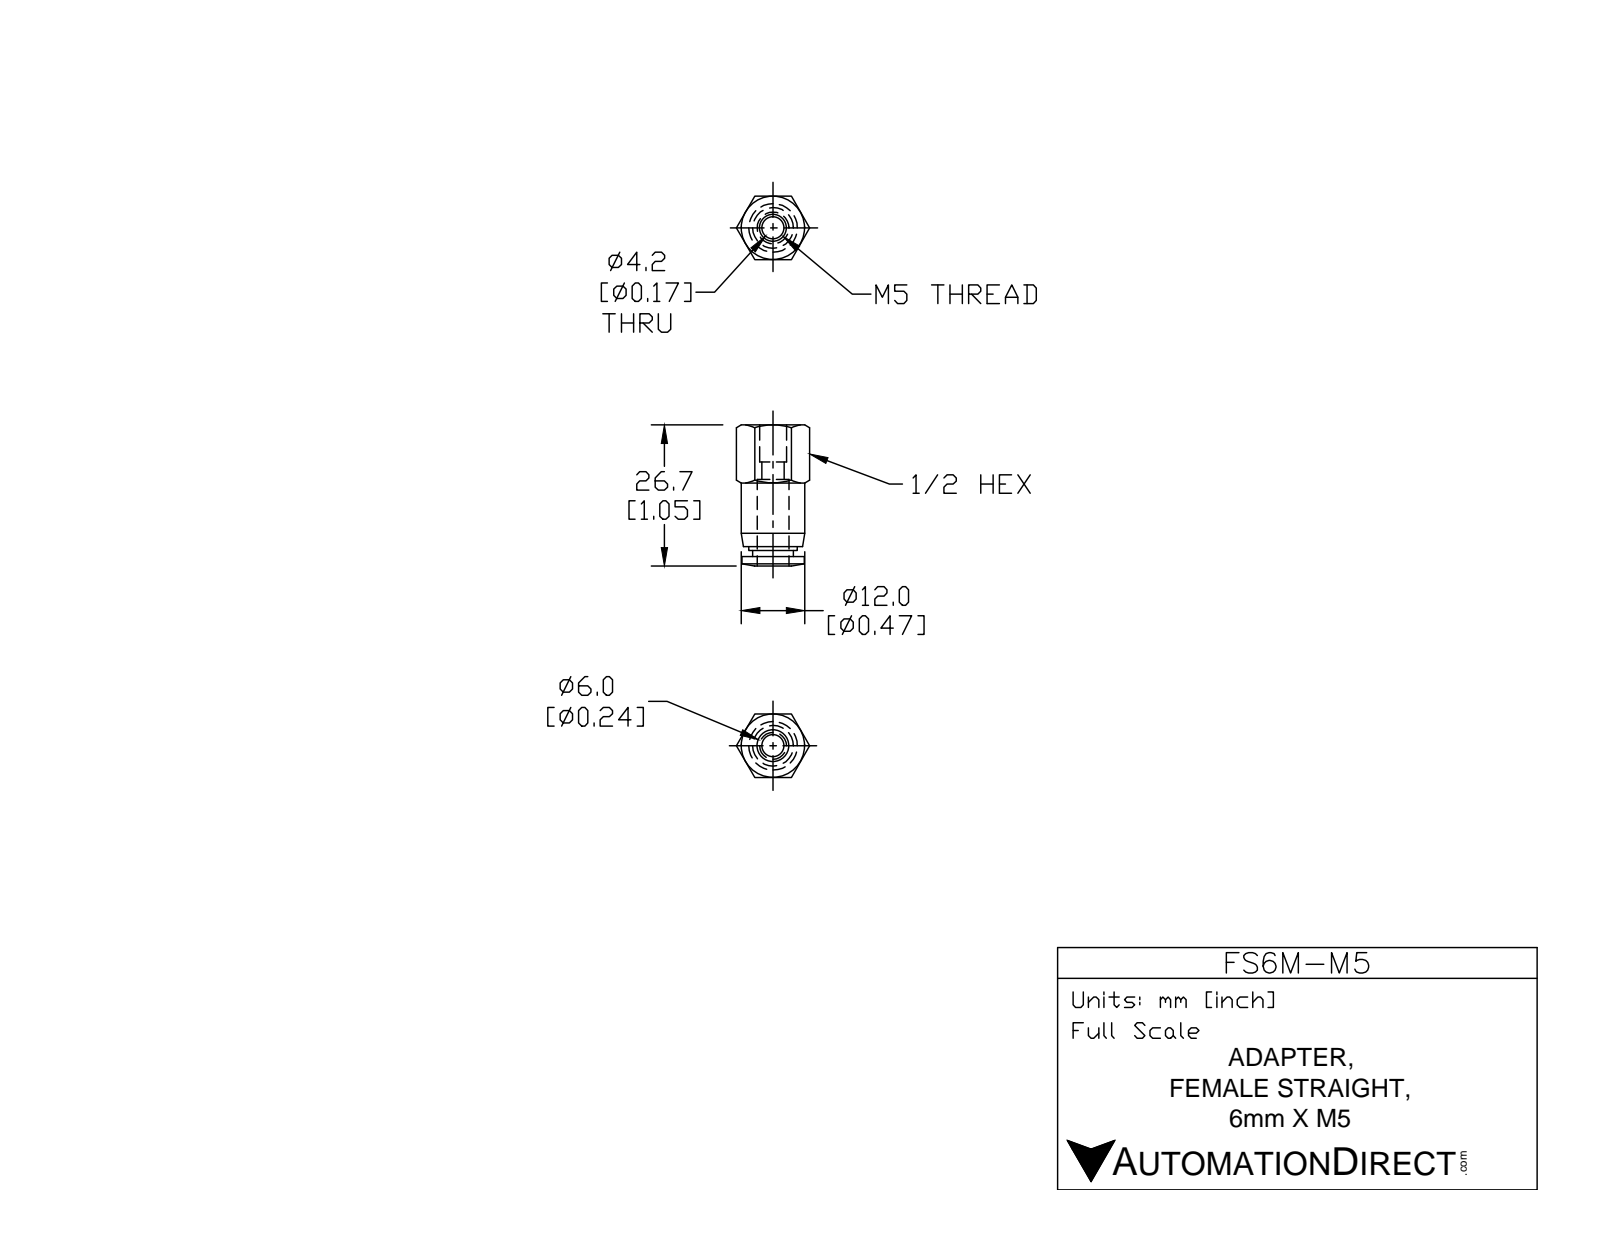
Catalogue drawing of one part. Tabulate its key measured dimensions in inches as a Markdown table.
| quantity | value |
| --- | --- |
| part name | FS6M-M5 |
| STEP written by | SolidWorks 2015 (AUTOMOTIVE_DESIGN) |
| units | inches |
| bodies | 1 solid, 46 faces (13 planar, 14 cylindrical, 19 other) |
| overall size | 1.051 × 0.546 × 0.472 |
| volume | 0.14 in³ |
| surface area | 2.8 in² |
| round holes (diameter × count) | 0.165 × 1, 0.197 × 1, 0.248 × 1 |
| round bosses / shafts (diameter × count) | 0.472 × 1, 0.465 × 1, 0.362 × 1, 0.303 × 1 |
| main face-to-face distances | 0.472, 0.98, 0.906, 0.075, 0.935, 0.03, 0.045, 0.406, 0.5, 0.53 |
